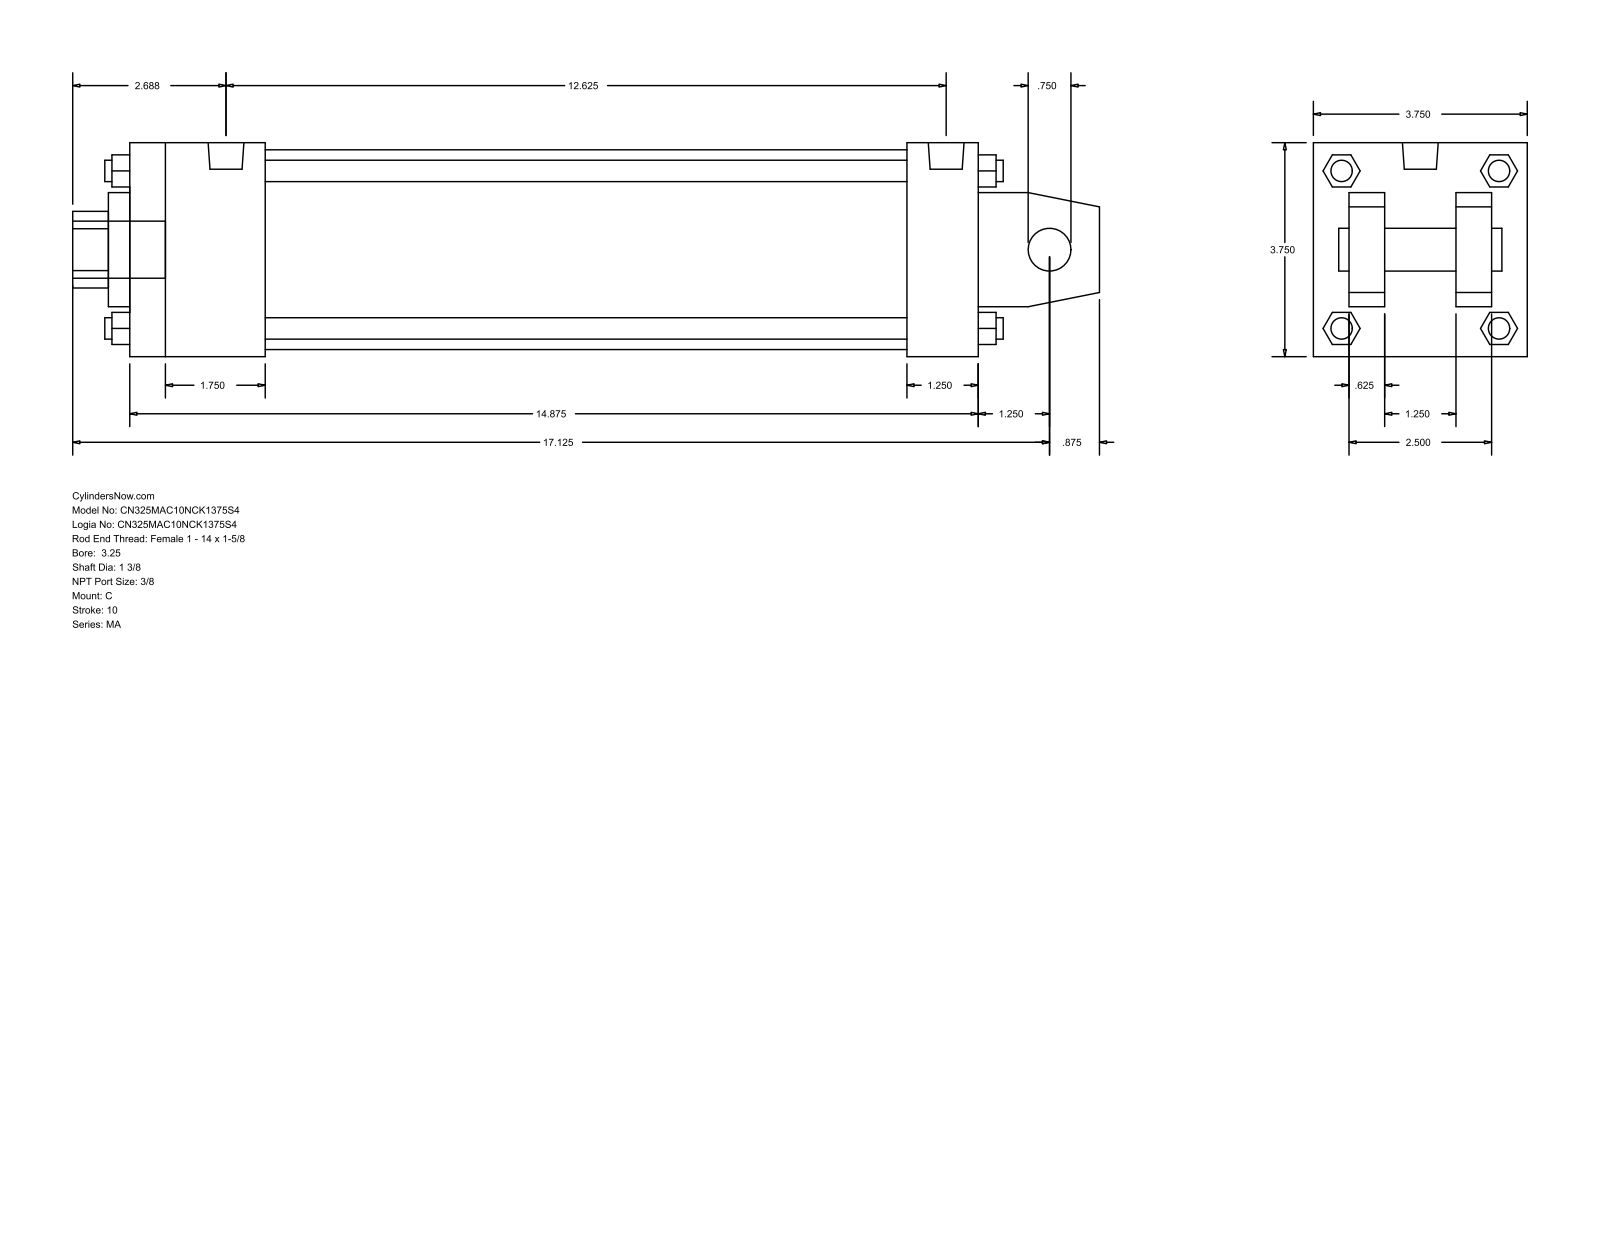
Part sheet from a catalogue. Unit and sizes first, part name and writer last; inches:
Units: inches
Overall size (bounding box): 18 × 3.75 × 3.75
Round holes (diameter × count): ⌀0.75 ×1, ⌀1.375 ×1, ⌀2 ×1, ⌀3.5 ×1
Round bosses / shafts (diameter × count): ⌀0.437 ×4, ⌀0.375 ×4, ⌀0.627 ×2, ⌀1 ×1
Partial cylindrical surfaces — rounded edges, fillets, slot ends (radius × count): R0.672 ×1
Main face-to-face distances: 3.75, 0.625, 2.5, 14.875, 1.25, 3.125, 1.875, 13.625, 1.25, 2.375
Bodies: 0 solids, 139 faces (108 planar, 31 cylindrical, 0 other)
Part name (STEP PRODUCT): MA_C__0325_1.375
STEP written by: GSSL Pune (CONFIG_CONTROL_DESIGN)
